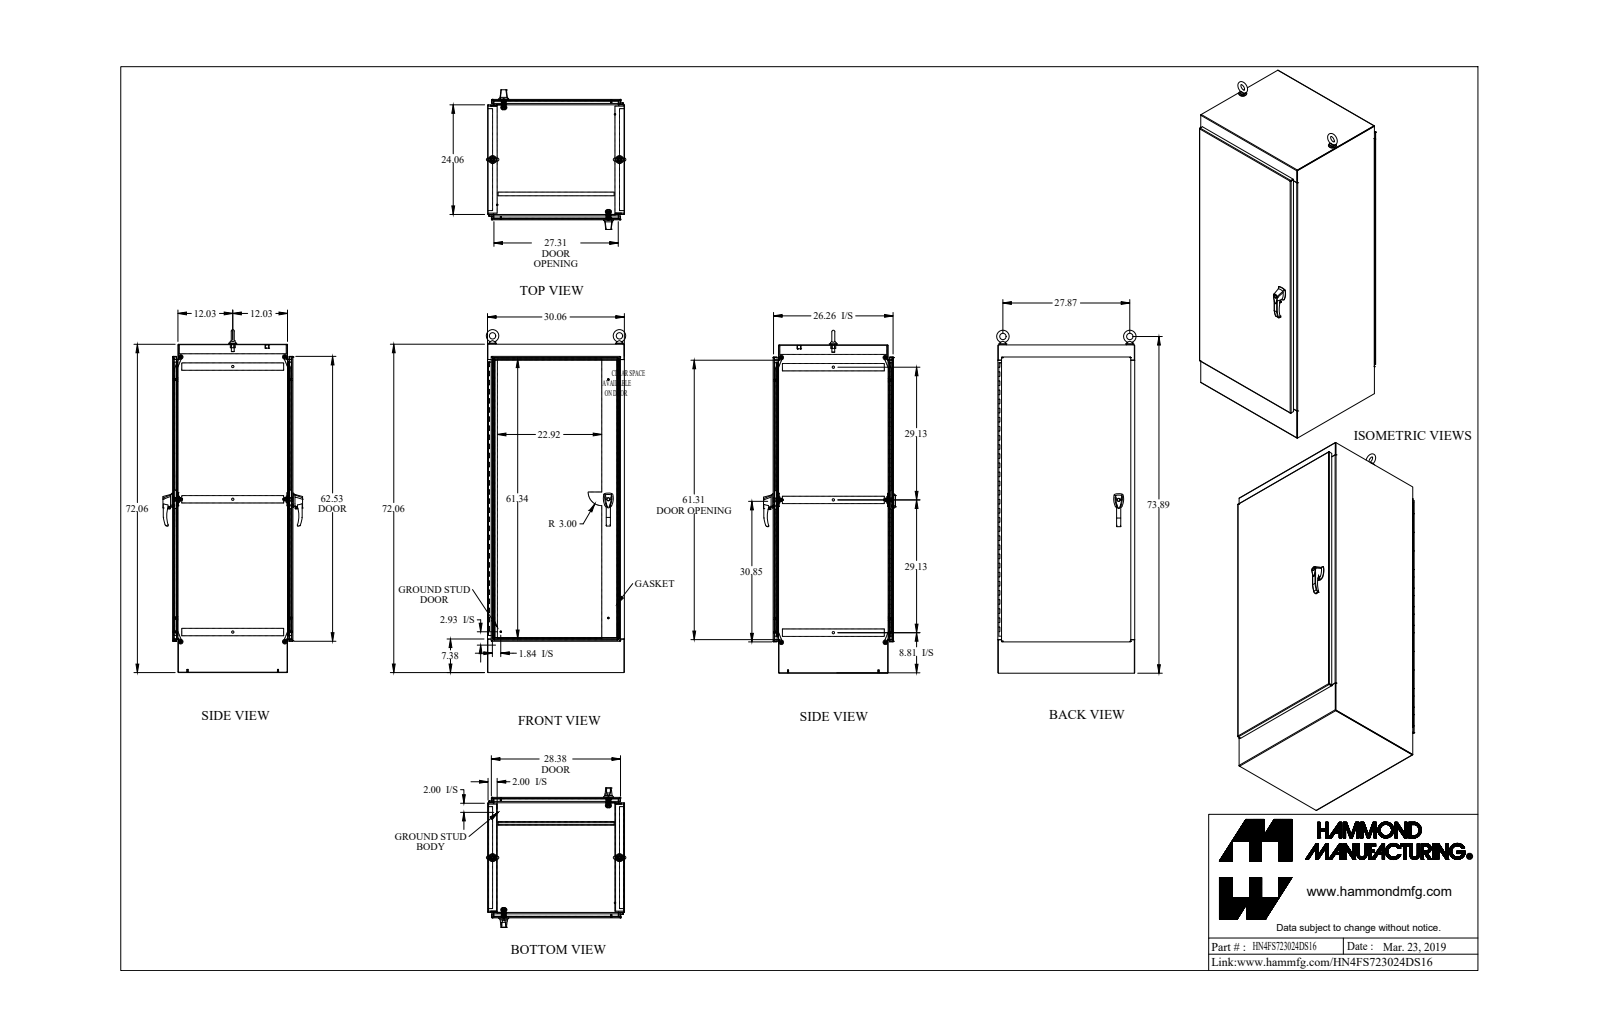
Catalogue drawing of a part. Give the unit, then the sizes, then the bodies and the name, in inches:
Units: inches
Overall size (bounding box): 75.256 × 30.664 × 30.604
Round holes (diameter × count): ⌀0.304 ×20, ⌀0.35 ×8, ⌀0.25 ×4, ⌀0.257 ×4, ⌀0.28 ×4, ⌀0.281 ×4, ⌀0.313 ×4, ⌀0.39 ×4, ⌀0.413 ×4, ⌀0.5 ×3, ⌀0.11 ×2, ⌀0.173 ×2
Round bosses / shafts (diameter × count): ⌀1 ×4, ⌀0.75 ×4, ⌀0.63 ×4, ⌀0.625 ×4, ⌀0.44 ×4, ⌀0.37 ×4, ⌀0.313 ×4, ⌀0.281 ×4
Partial cylindrical surfaces — rounded edges, fillets, slot ends (radius × count): R0.125 ×44, R0.043 ×42, R0.138 ×36, R0.018 ×32, R0.048 ×26, R0.143 ×26, R0.5 ×26, R0.06 ×21
Main face-to-face distances: 0.095, 26.339, 29.965, 29.87, 1.187, 25.152, 26.244, 26.434, 30.06, 71.965
Hole centre spacings: 6, 28.935, 12, 30.745, 18, 33.545, 24, 37.111
Volume: 1 153 in³ · Surface area: 24 285 in²
Bodies: 88 solids, 3200 faces (1433 planar, 1499 cylindrical, 268 other)
Part name (STEP PRODUCT): HN4FS723024DS16
STEP written by: SolidWorks 2018 (AUTOMOTIVE_DESIGN)
